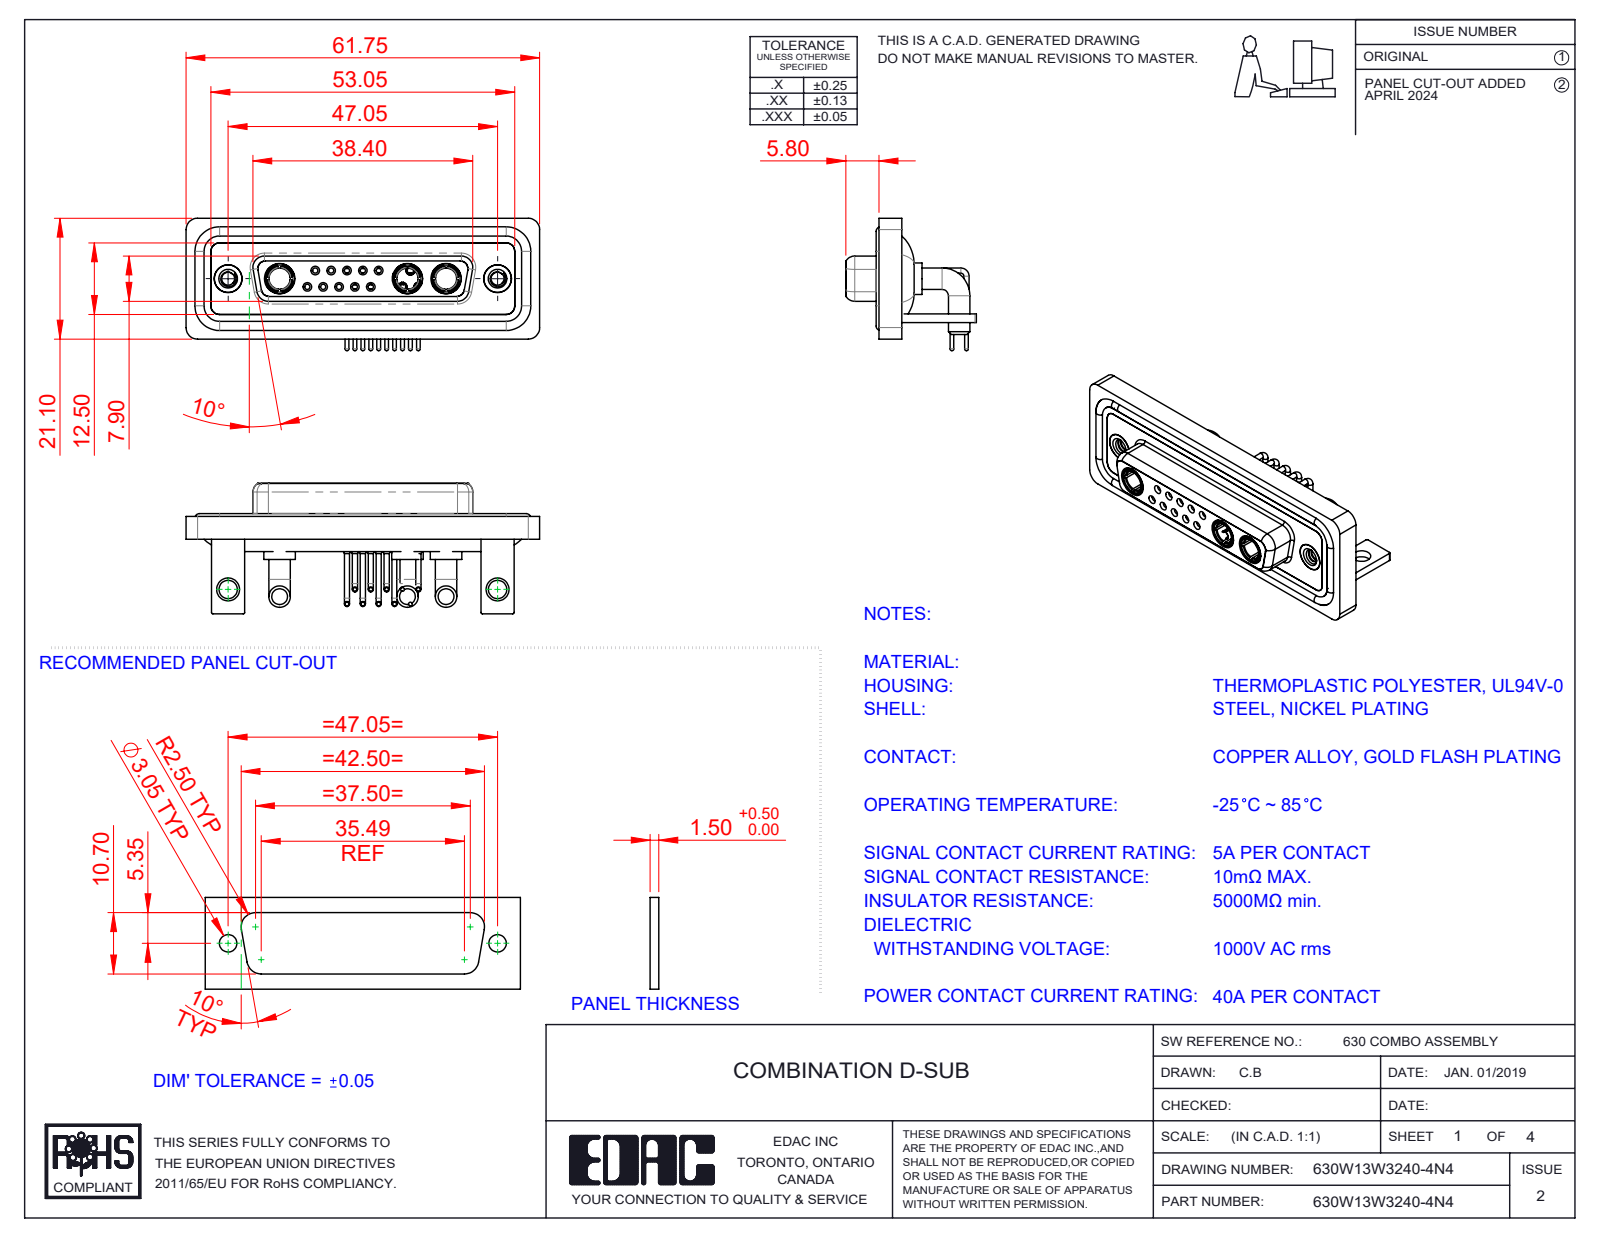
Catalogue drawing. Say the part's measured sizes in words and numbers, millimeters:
The part is named "630Combo Housing_13W3; 630Combo Stabilizer Bracket_50 Contacts; 630Combo Waterproof Housing_25 Contacts; 630W13W3140-4N4 (+6 more)". Its 3-D file was written by "SolidWorks 2023 (CONFIG_CONTROL_DESIGN)". It is 25 solids with 1198 faces: 362 planar, 517 cylindrical and 319 other. Overall it measures 61.75 by 23.12 by 22.8 millimeters. Its volume is 9 055 cubic millimeters and its surface area 15 163 square millimeters. Round holes: 10 of diameter 0.9, 10 of diameter 1.1, 10 of diameter 1.5, 10 of diameter 2, 5 of diameter 1.6, 5 of diameter 1.7, 5 of diameter 4.85, 3 of diameter 3.7, 3 of diameter 5.3, 2 of diameter 2.26, 2 of diameter 3.2, 2 of diameter 4. Round bosses or shafts: 15 of diameter 0.9, 12 of diameter 1.6, 10 of diameter 0.65, 6 of diameter 3.75, 5 of diameter 2, 5 of diameter 1.5, 3 of diameter 5.5, 3 of diameter 5.2. Partial cylindrical surfaces (rounded edges, fillets, slot ends): 19 of radius 2, 18 of radius 1.5, 16 of radius 0.25, 8 of radius 1.35, 8 of radius 1.6, 5 of radius 0.5, 4 of radius 0.6, 4 of radius 0.65. The main face-to-face distances are 0.4, 1.8, 2.9, 3.7, 1.5, 4.1, 1.1, 1.4, 1.6, 3.1. The hole center spacings are 3.16, 2.77, 5.54, 5.04, 8.31, 5.03, 7.49, 11.08.
